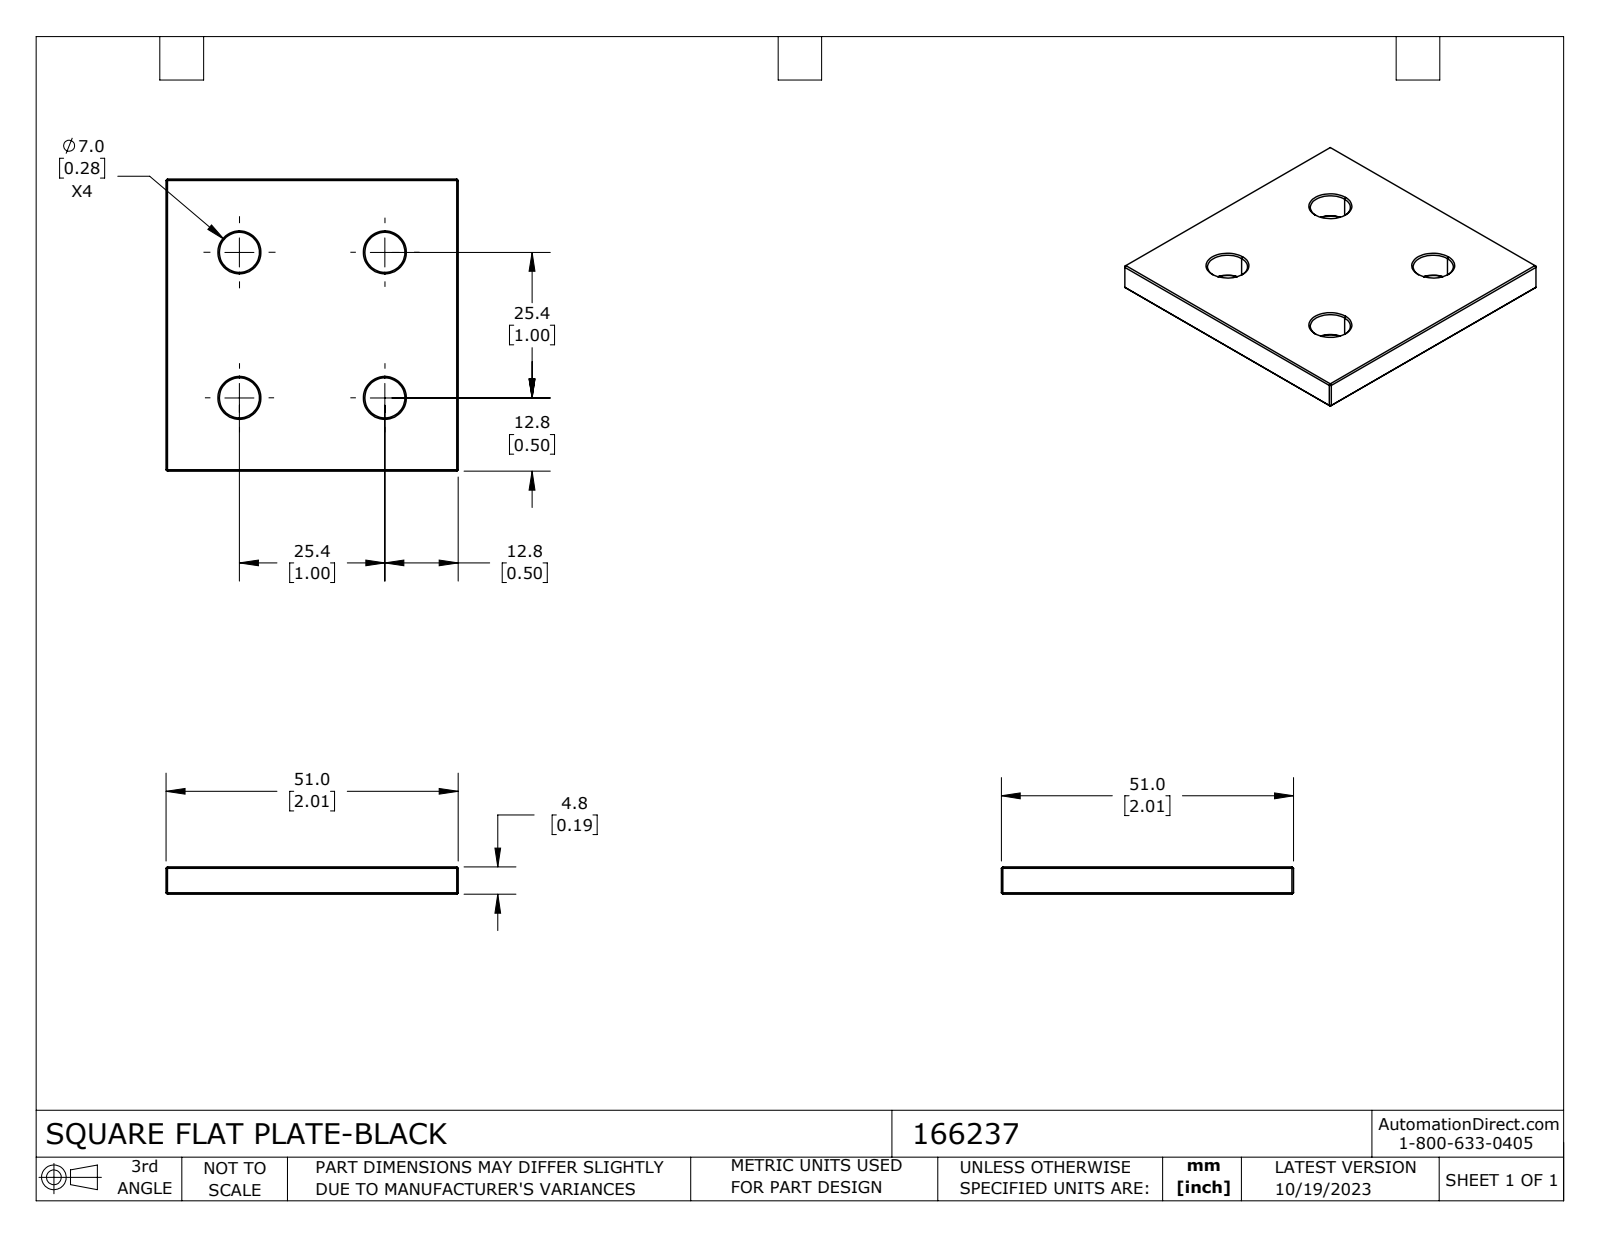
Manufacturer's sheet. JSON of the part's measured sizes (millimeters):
{"part_name": "166237", "step_written_by": "SolidWorks 2023 (CONFIG_CONTROL_DESIGN)", "units": "millimeters", "bodies": {"solids": 1, "faces": 50, "planar": 26, "cylindrical": 8, "other": 16}, "overall_size": [51, 51, 4.76], "volume_mm3": 11635, "surface_area_mm2": 6197, "round_holes": [[7, 4]], "face_to_face_distances": [4.76, 51, 39.07, 71.76, 61.03], "hole_center_spacings": [25.4, 35.92]}
